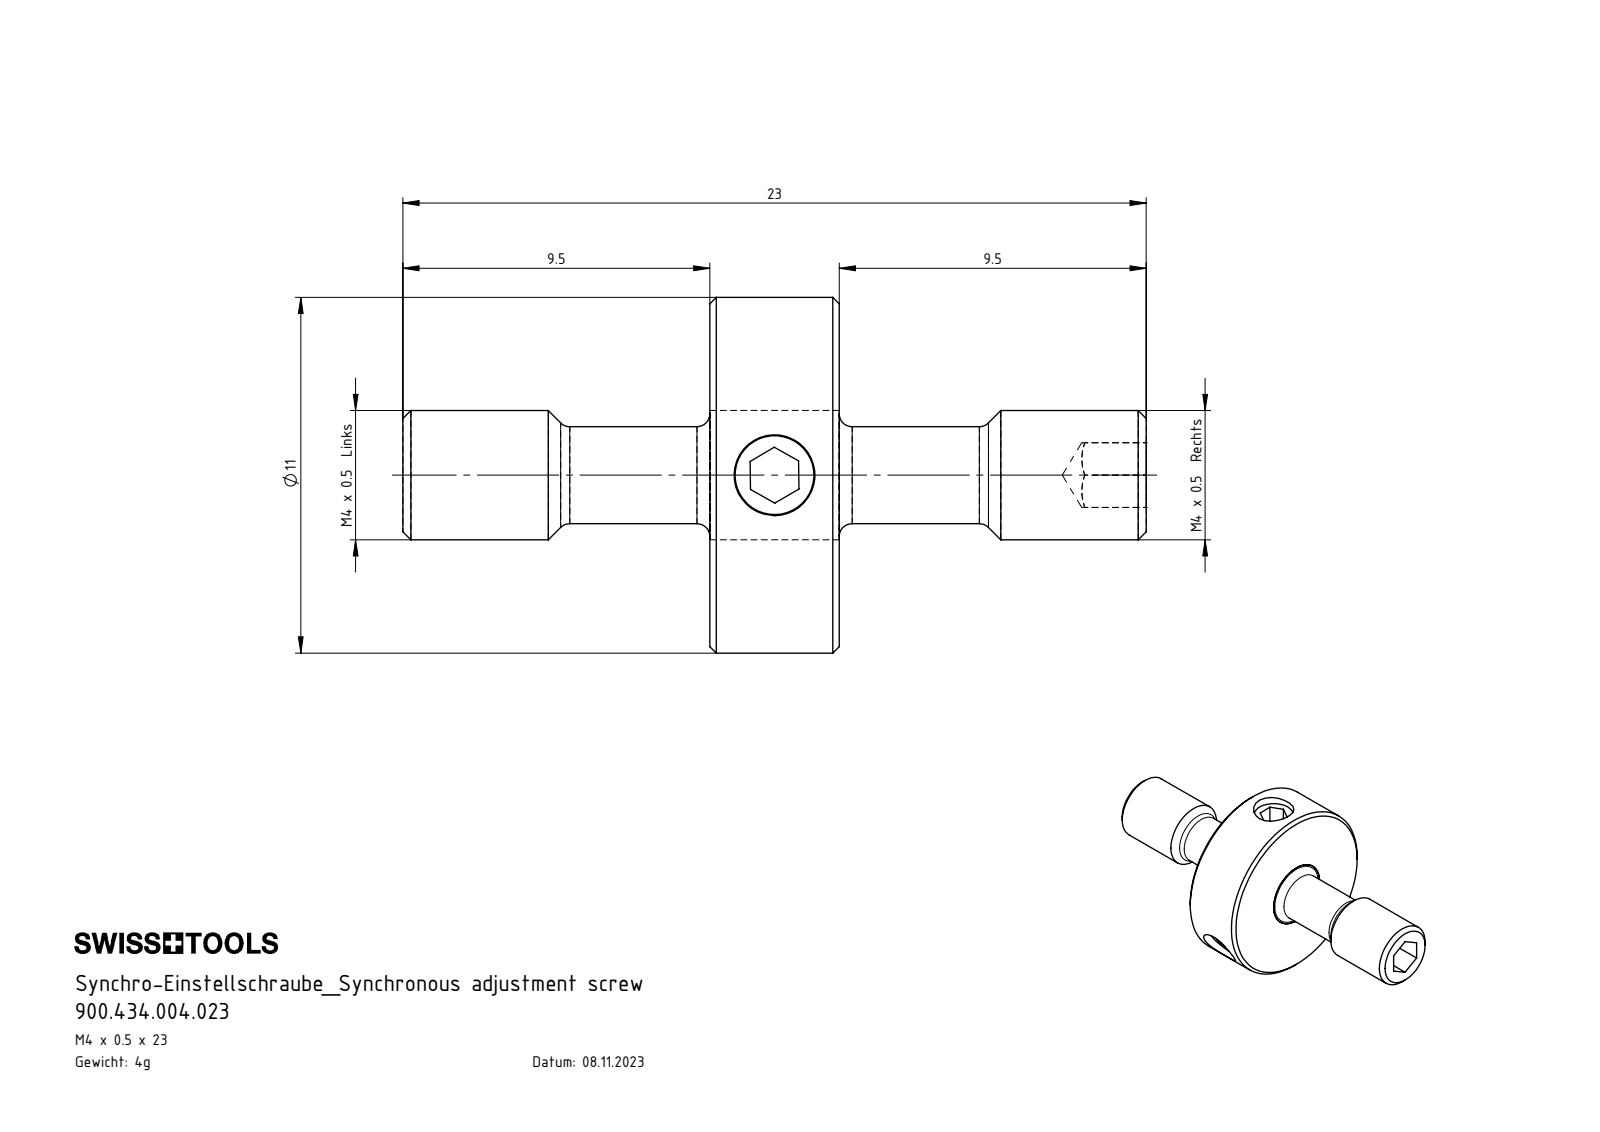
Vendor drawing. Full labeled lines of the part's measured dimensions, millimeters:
Part name (STEP PRODUCT): Z25-ER3.001.023_A; Z25-ER3.002.004_A; 900.434.004.023; ISO 4026 - M3 x 3
STEP written by: SolidWorks 2022 (AUTOMOTIVE_DESIGN)
Units: millimetres
Bodies: 5 solids, 99 faces (39 planar, 26 cylindrical, 34 other)
Overall size (bounding box): 23 × 11 × 11
Volume: 553 mm³ · Surface area: 853 mm²
Round holes (diameter × count): ⌀2.5 ×3
Round bosses / shafts (diameter × count): ⌀3 ×4, ⌀11 ×1, ⌀4 ×1
Main face-to-face distances: 4, 9.5, 13.5, 1.5, 2, 3, 10.75, 12.25, 1.25, 2.75
